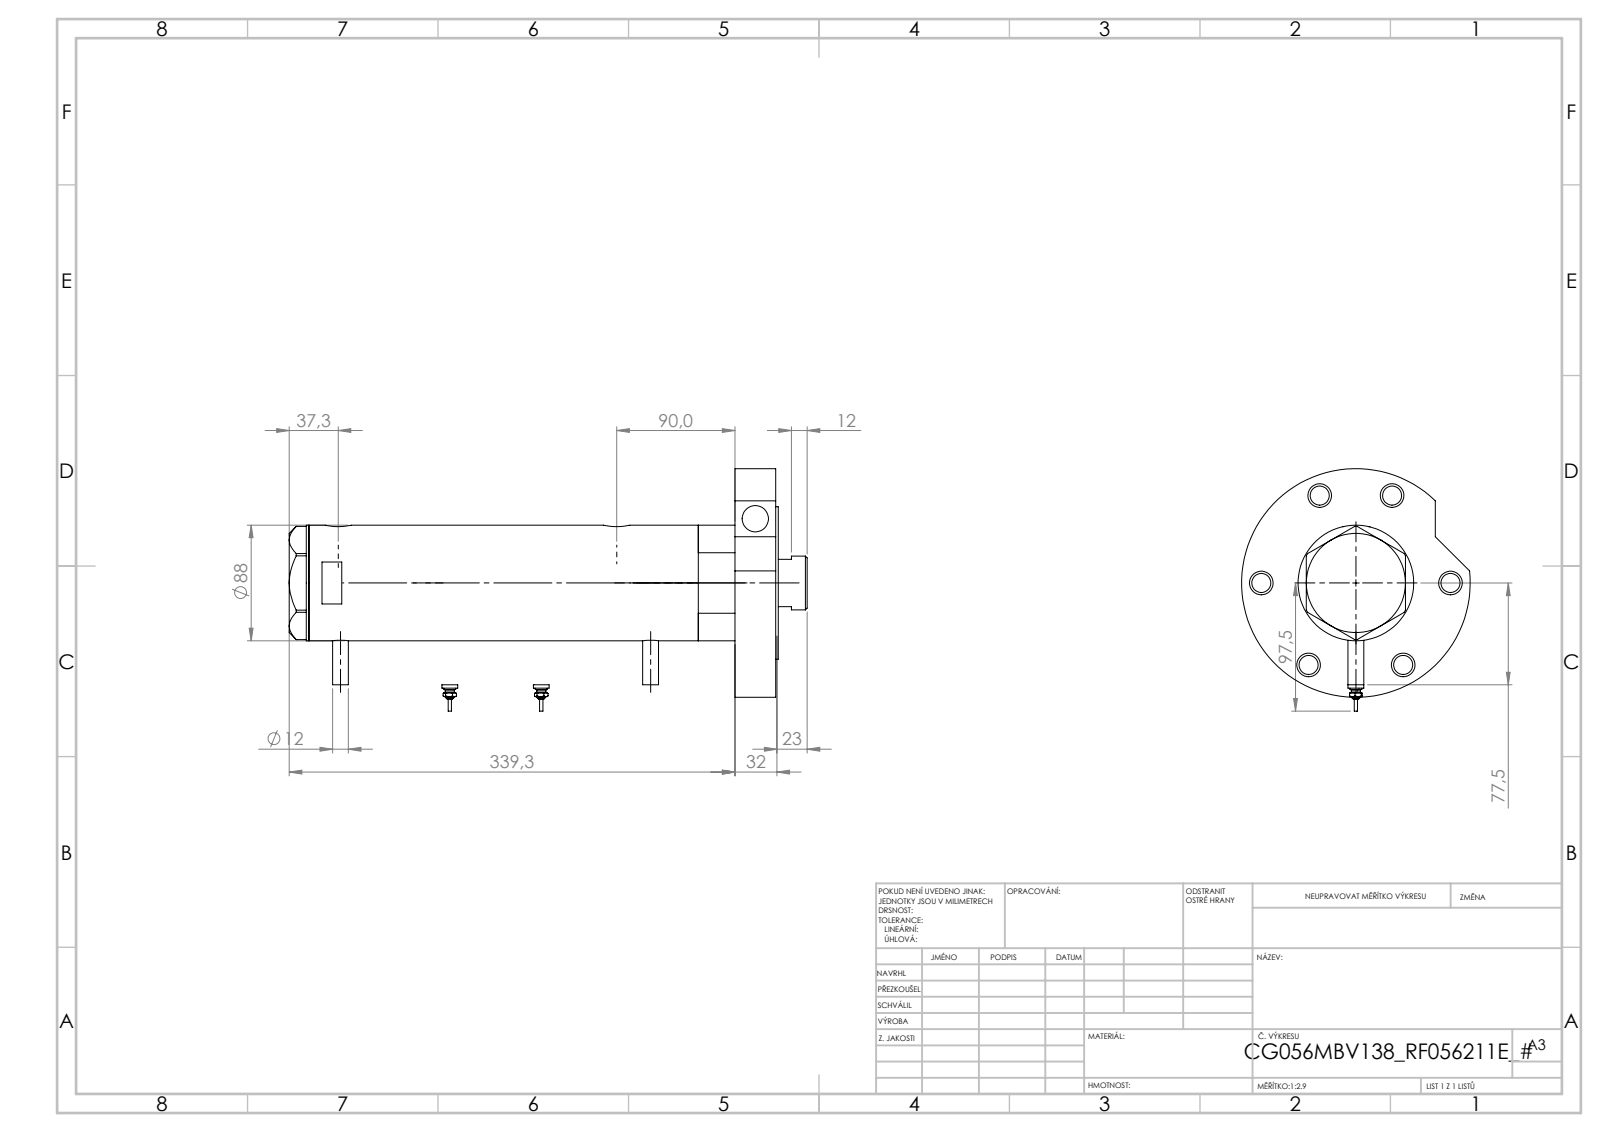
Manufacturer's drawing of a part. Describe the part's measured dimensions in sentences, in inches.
The part is named "V270CG_BACK; V270CG_VC; V270CG_FRONT; V270CG_RF211E (+2 more)". Its 3-D file was written by "SolidWorks 2019 (CONFIG_CONTROL_DESIGN)". It is 7 solids with 257 faces: 91 planar, 102 cylindrical and 64 other. Overall it measures 15.524 by 7.264 by 6.85 inches. Its volume is 157.1 cubic inches and its surface area 559.9 square inches. Round holes: 7 of diameter 0.571, 6 of diameter 0.709, 3 of diameter 0.787, 2 of diameter 0.492, 2 of diameter 0.518, 1 of diameter 1.654, 1 of diameter 1.713, 1 of diameter 2.205, 1 of diameter 2.362, 1 of diameter 2.953, 1 of diameter 3.15. Round bosses or shafts: 4 of diameter 0.472, 2 of diameter 0.354, 2 of diameter 0.276, 2 of diameter 0.177, 2 of diameter 0.098, 1 of diameter 6.85, 1 of diameter 4.567, 1 of diameter 3.465. The main face-to-face distances are 1.22, 0.079, 14.067, 9.228, 12.768, 13.988, 1.299, 3.539, 4.76, 4.839. The hole center spacings are 2.835, 3.15, 4.714, 4.91, 5.085, 5.657, 0.067, 1.016.
